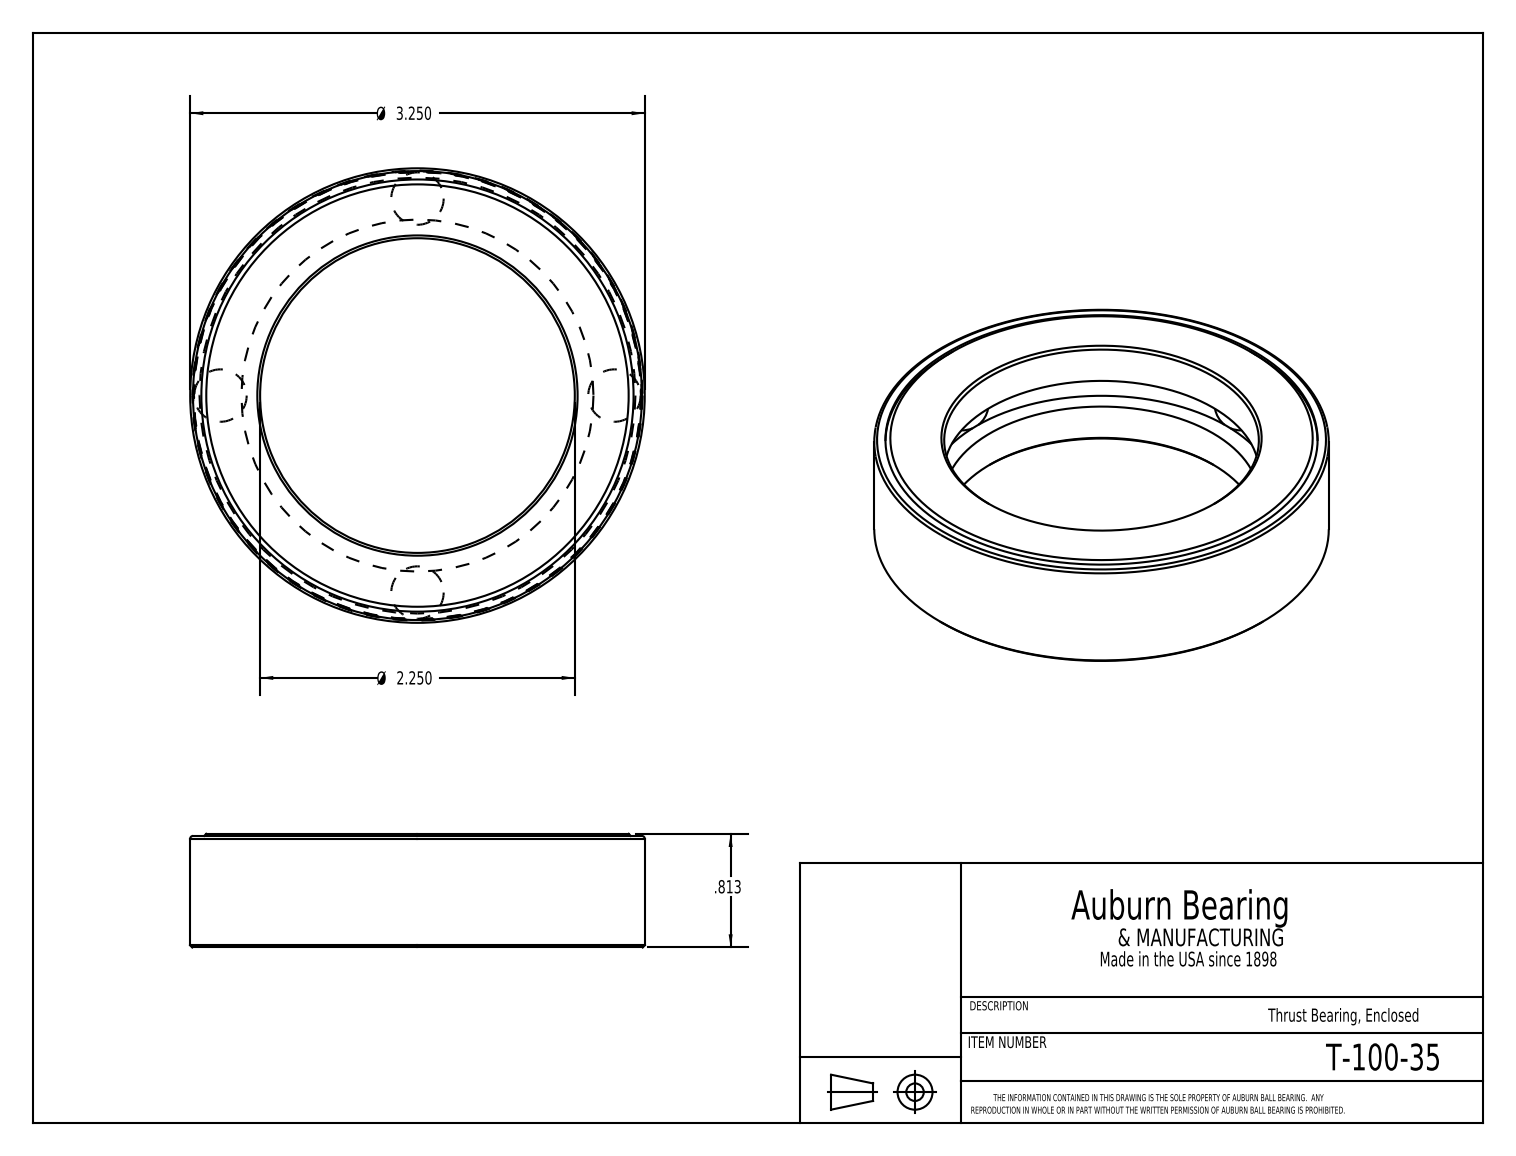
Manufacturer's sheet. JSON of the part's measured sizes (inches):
{"part_name": "T-100-35", "step_written_by": "SolidWorks 2016 (CONFIG_CONTROL_DESIGN)", "units": "inches", "bodies": {"solids": 6, "faces": 28, "planar": 9, "cylindrical": 7, "other": 12}, "overall_size": [3.25, 3.25, 0.813], "volume_in3": 2.361, "surface_area_in2": 40.05, "round_holes": [[2.25, 1], [3.09, 1], [3.21, 1]], "round_bosses_or_shafts": [[3.25, 1], [3.196, 1]], "face_to_face_distances": [0.813, 0.294, 0.519, 0.225, 0.798, 0.504, 0.279, 0.015, 0.778, 0.484]}
